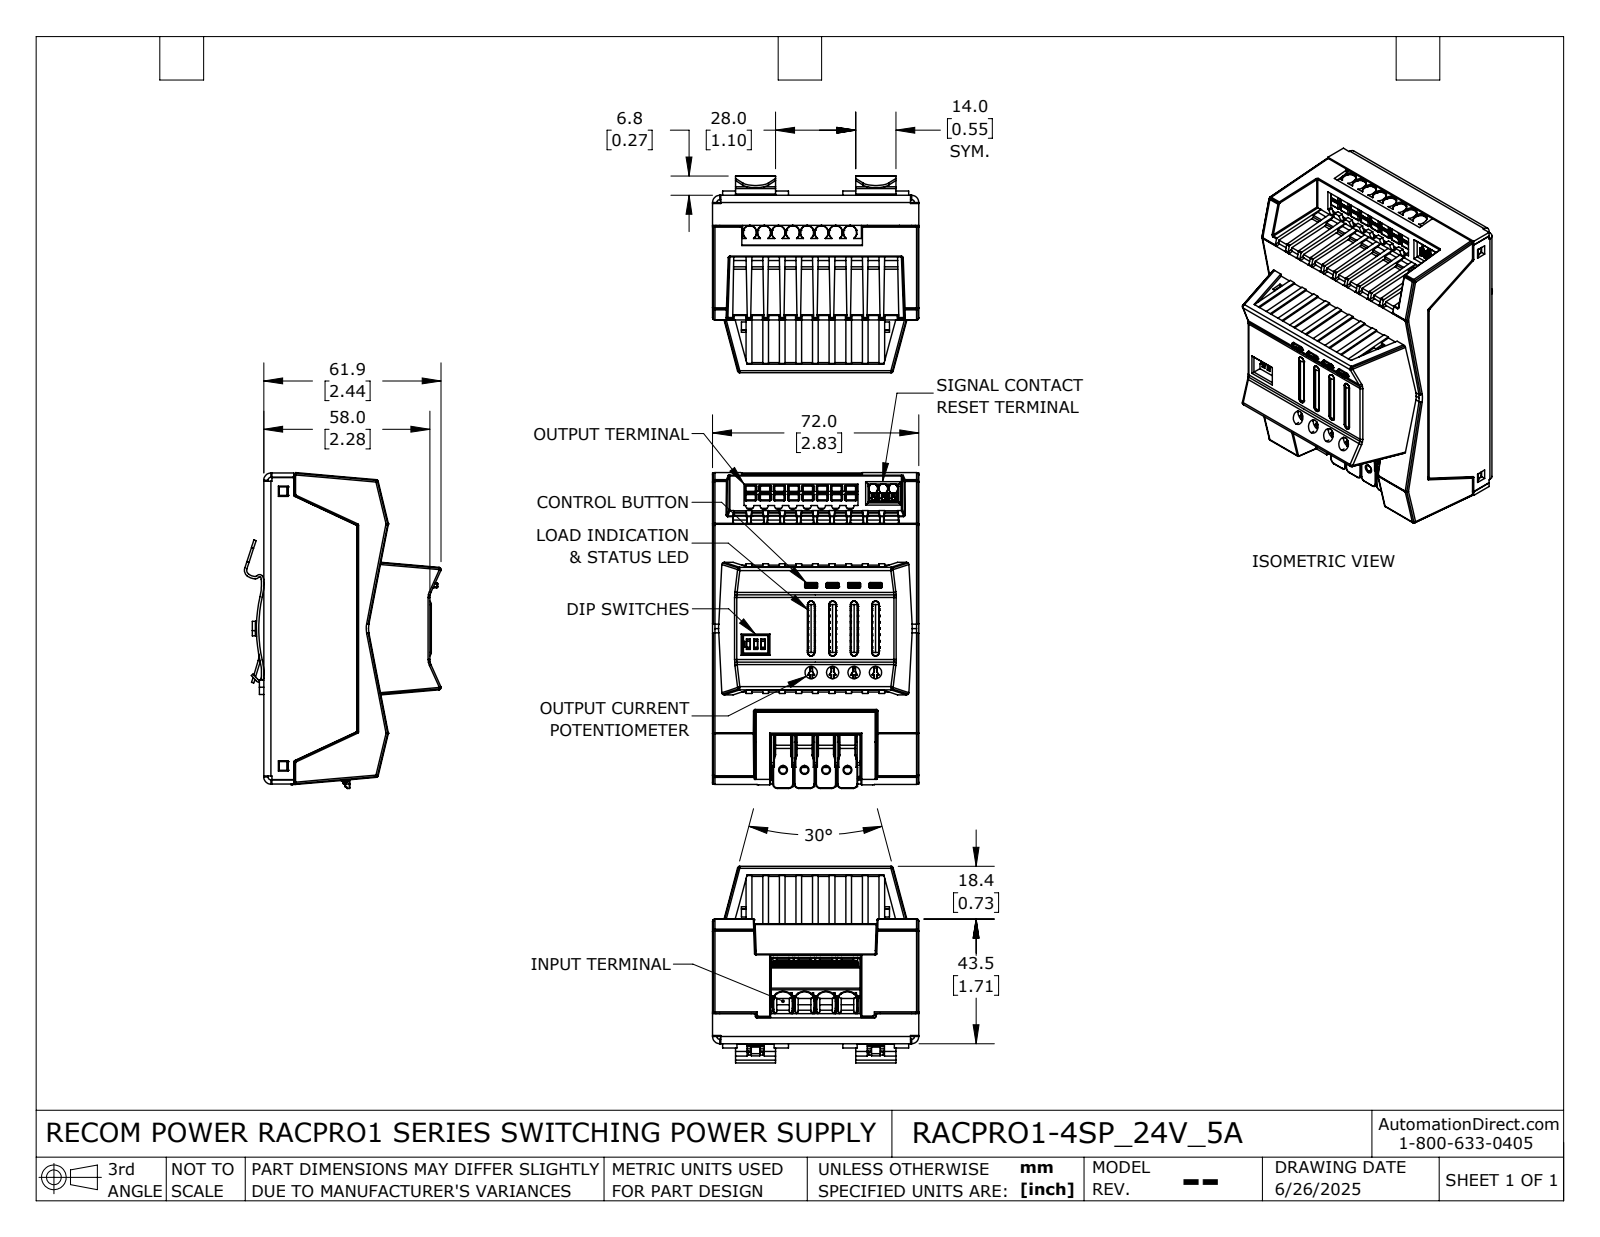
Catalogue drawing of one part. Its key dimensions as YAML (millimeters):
part_name: "RACPRO1-4SP_24V_5A"
step_written_by: "SolidWorks 2024 (AUTOMOTIVE_DESIGN)"
units: millimeters
bodies: {solids: 3, faces: 4294, planar: 1978, cylindrical: 1474, other: 842}
overall_size: [110.2, 72, 68.7]
volume: 325000
surface_area: 80390
round_holes:
  - {diameter: 4.3, count: 6}
  - {diameter: 2, count: 4}
  - {diameter: 2.5, count: 4}
  - {diameter: 3.4, count: 3}
  - {diameter: 1.5, count: 2}
  - {diameter: 1.6, count: 2}
  - {diameter: 3.5, count: 2}
  - {diameter: 1, count: 1}
  - {diameter: 2, count: 1}
  - {diameter: 2.1, count: 1}
round_bosses_or_shafts:
  - {diameter: 5, count: 4}
  - {diameter: 5.1, count: 2}
  - {diameter: 1.5, count: 2}
  - {diameter: 3.3, count: 1}
  - {diameter: 2, count: 1}
partial_cylinders:
  - {radius: 0.2, count: 291}
  - {radius: 0.4, count: 79}
  - {radius: 0.5, count: 61}
  - {radius: 1, count: 50}
  - {radius: 0.3, count: 46}
  - {radius: 0.2, count: 29}
  - {radius: 0.8, count: 29}
  - {radius: 2.5, count: 21}
face_to_face_distances: [1.5, 1, 2.5, 30, 31, 32.5, 30.2, 31.2, 32.7, 72]
hole_center_spacings: [7.5, 15, 22.4, 35.4, 28.9, 34.1, 38.2, 42]
